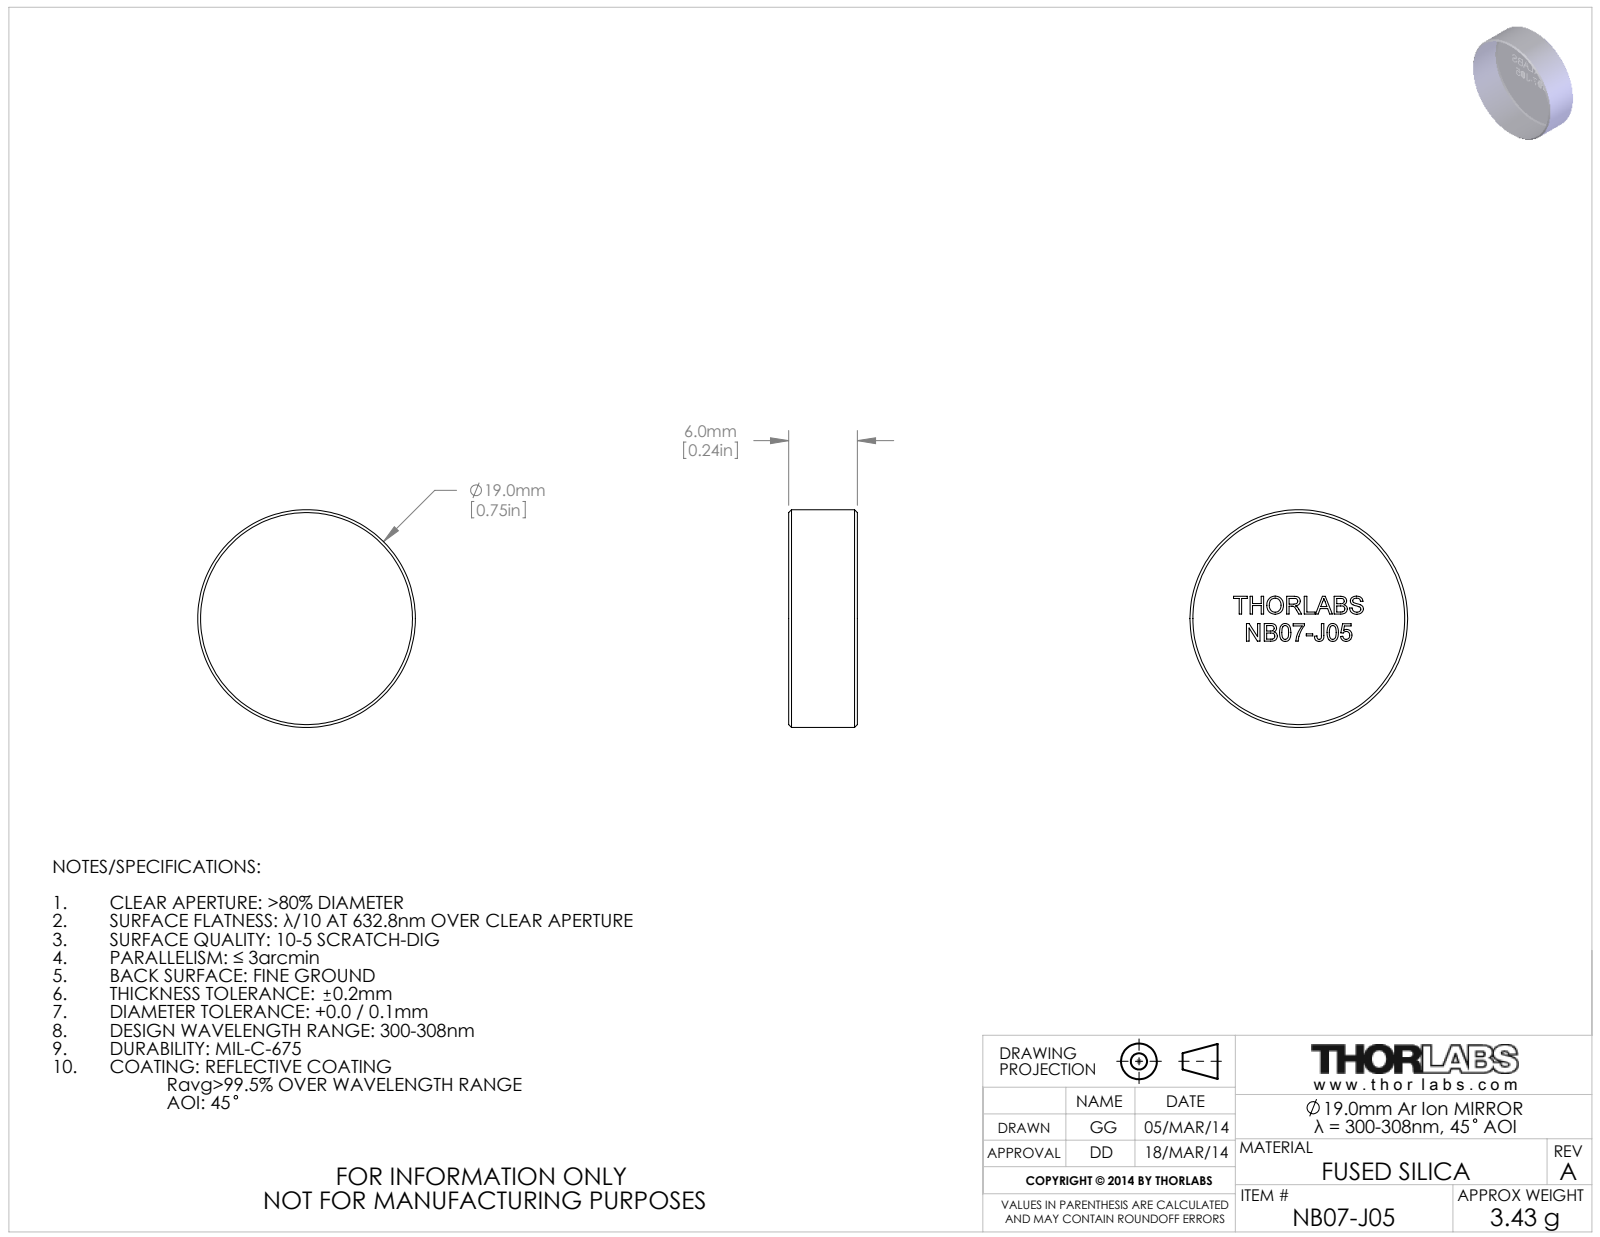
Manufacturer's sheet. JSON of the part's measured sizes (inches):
{"part_name": "TTN024116-E0W", "step_written_by": "SolidWorks 2012 (CONFIG_CONTROL_DESIGN)", "units": "inches", "bodies": {"solids": 1, "faces": 219, "planar": 125, "cylindrical": 2, "other": 92}, "overall_size": [0.748, 0.748, 0.236], "volume_in3": 0.104, "surface_area_in2": 1.407, "round_bosses_or_shafts": [[0.748, 1]], "face_to_face_distances": [0.236, 0.061, 0.163, 0.094, 0.076, 0.038, 0.012, 0.093, 0.086, 0.054]}
